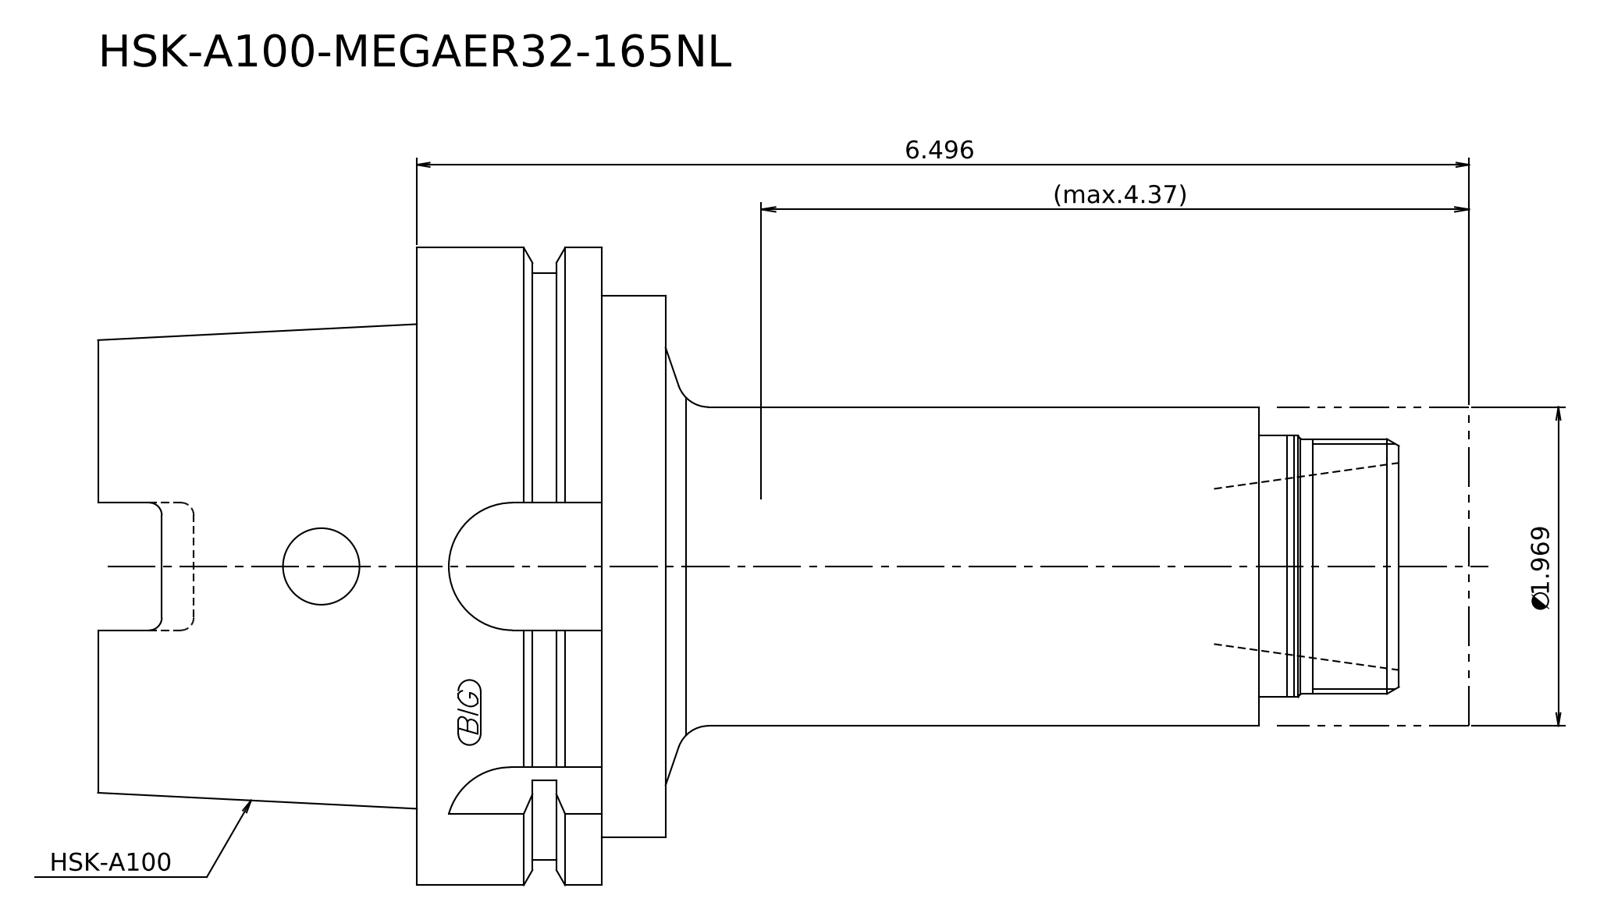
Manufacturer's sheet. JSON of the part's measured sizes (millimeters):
{"step_written_by": "Kubotek KeyCreator 2011 V10.0.2 (22737) (automotive_design)", "units": "millimeters", "bodies": {"solids": 2, "faces": 24, "planar": 10, "cylindrical": 8, "other": 6}, "overall_size": [215, 100, 100], "volume_mm3": 766603, "surface_area_mm2": 65421, "round_bosses_or_shafts": [[100, 1], [92, 1], [85, 1], [50, 1], [41, 1], [40, 1]], "face_to_face_distances": [50, 29, 79, 10, 39, 89, 95.8, 105.8, 134.8, 184.8]}
